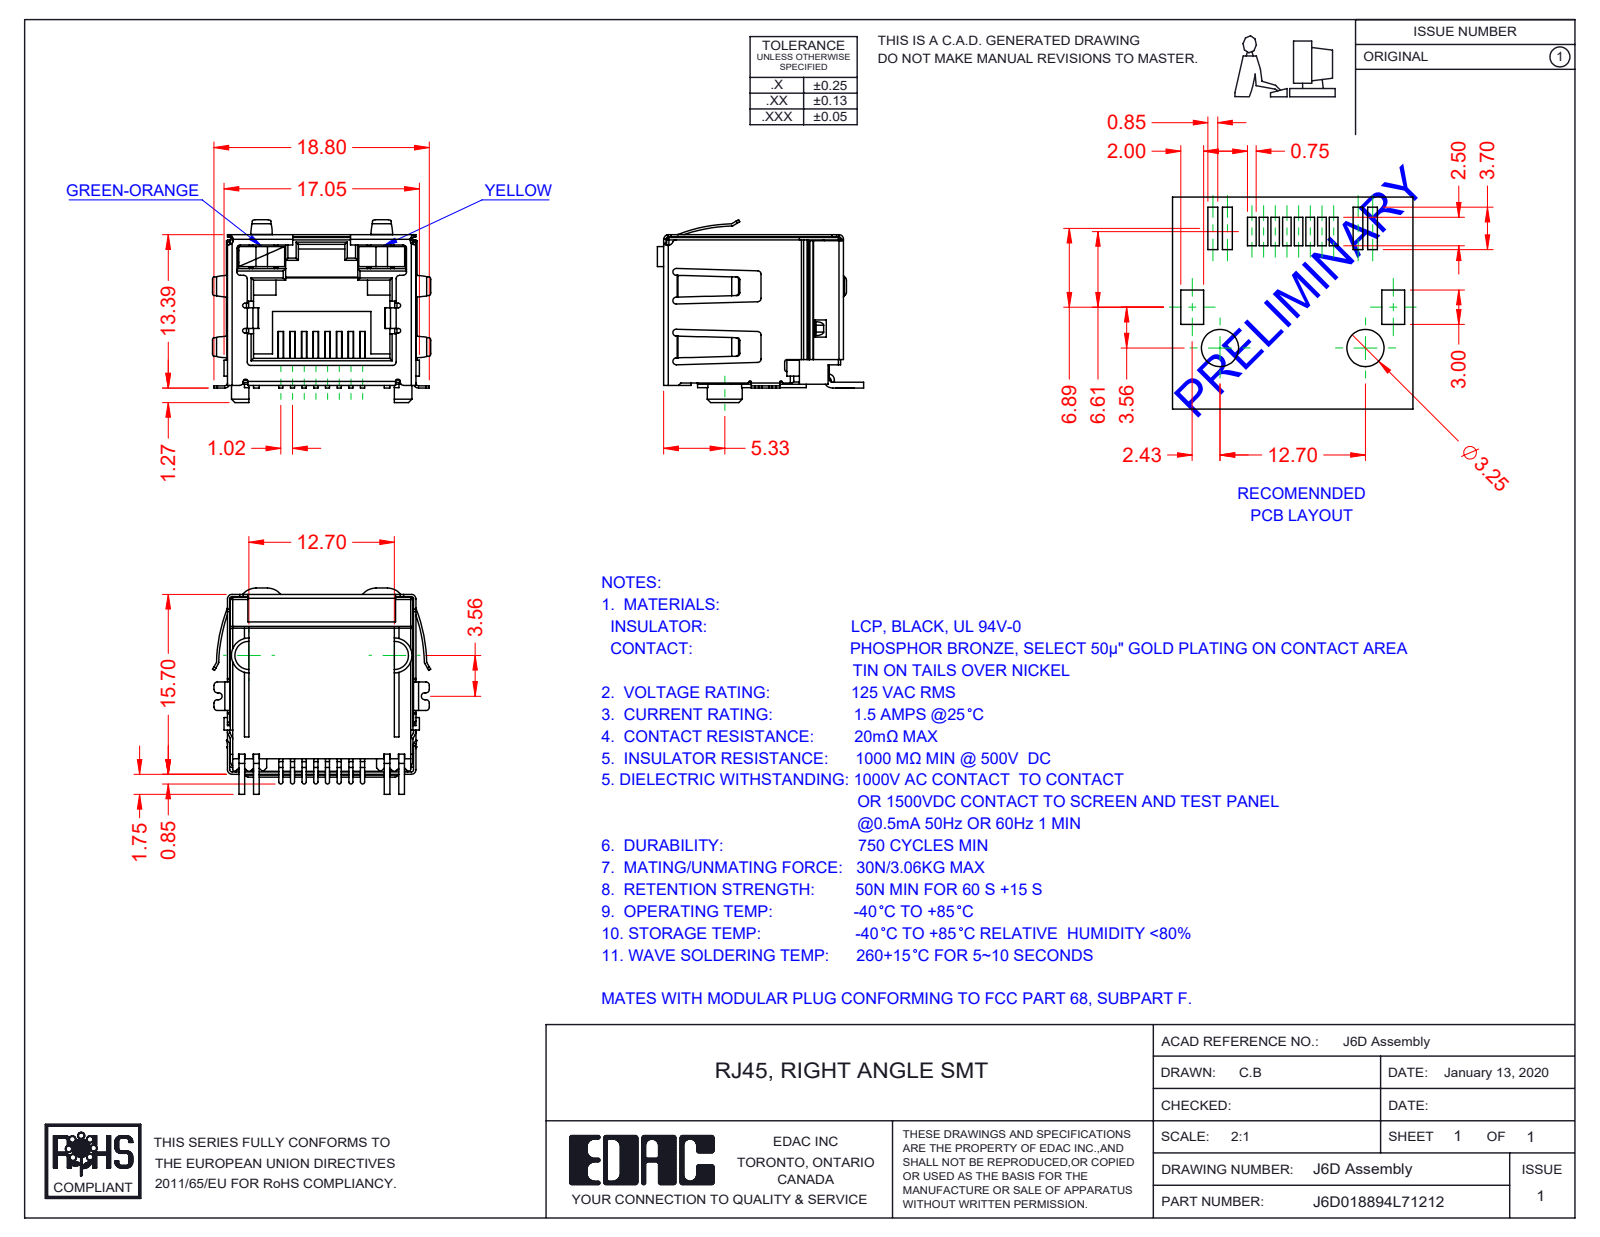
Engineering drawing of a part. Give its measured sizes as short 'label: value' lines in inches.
name: 6D LED LH_7-Green-Orange; 6D Shield_LED - EMI; 6D Contacts; 6D LED RH_1-Yellow (+2 more)
written by: SolidWorks 2016 (CONFIG_CONTROL_DESIGN)
unit: in
bodies: 12 solids, 1031 faces (702 planar, 284 cylindrical, 45 other)
size: 0.75 × 0.709 × 0.628
volume: 0.109 in³; area: 7.434 in²
rounds: 55× R0.012, 40× R0.008, 19× R0.016, 16× R0.01, 12× R0.004, 8× R0.006, 8× R0.007, 6× R0.02
face distances: 0.63, 0.638, 0.64, 0.089, 0.039, 0.628, 0.504, 0.018, 0.514, 0.417
